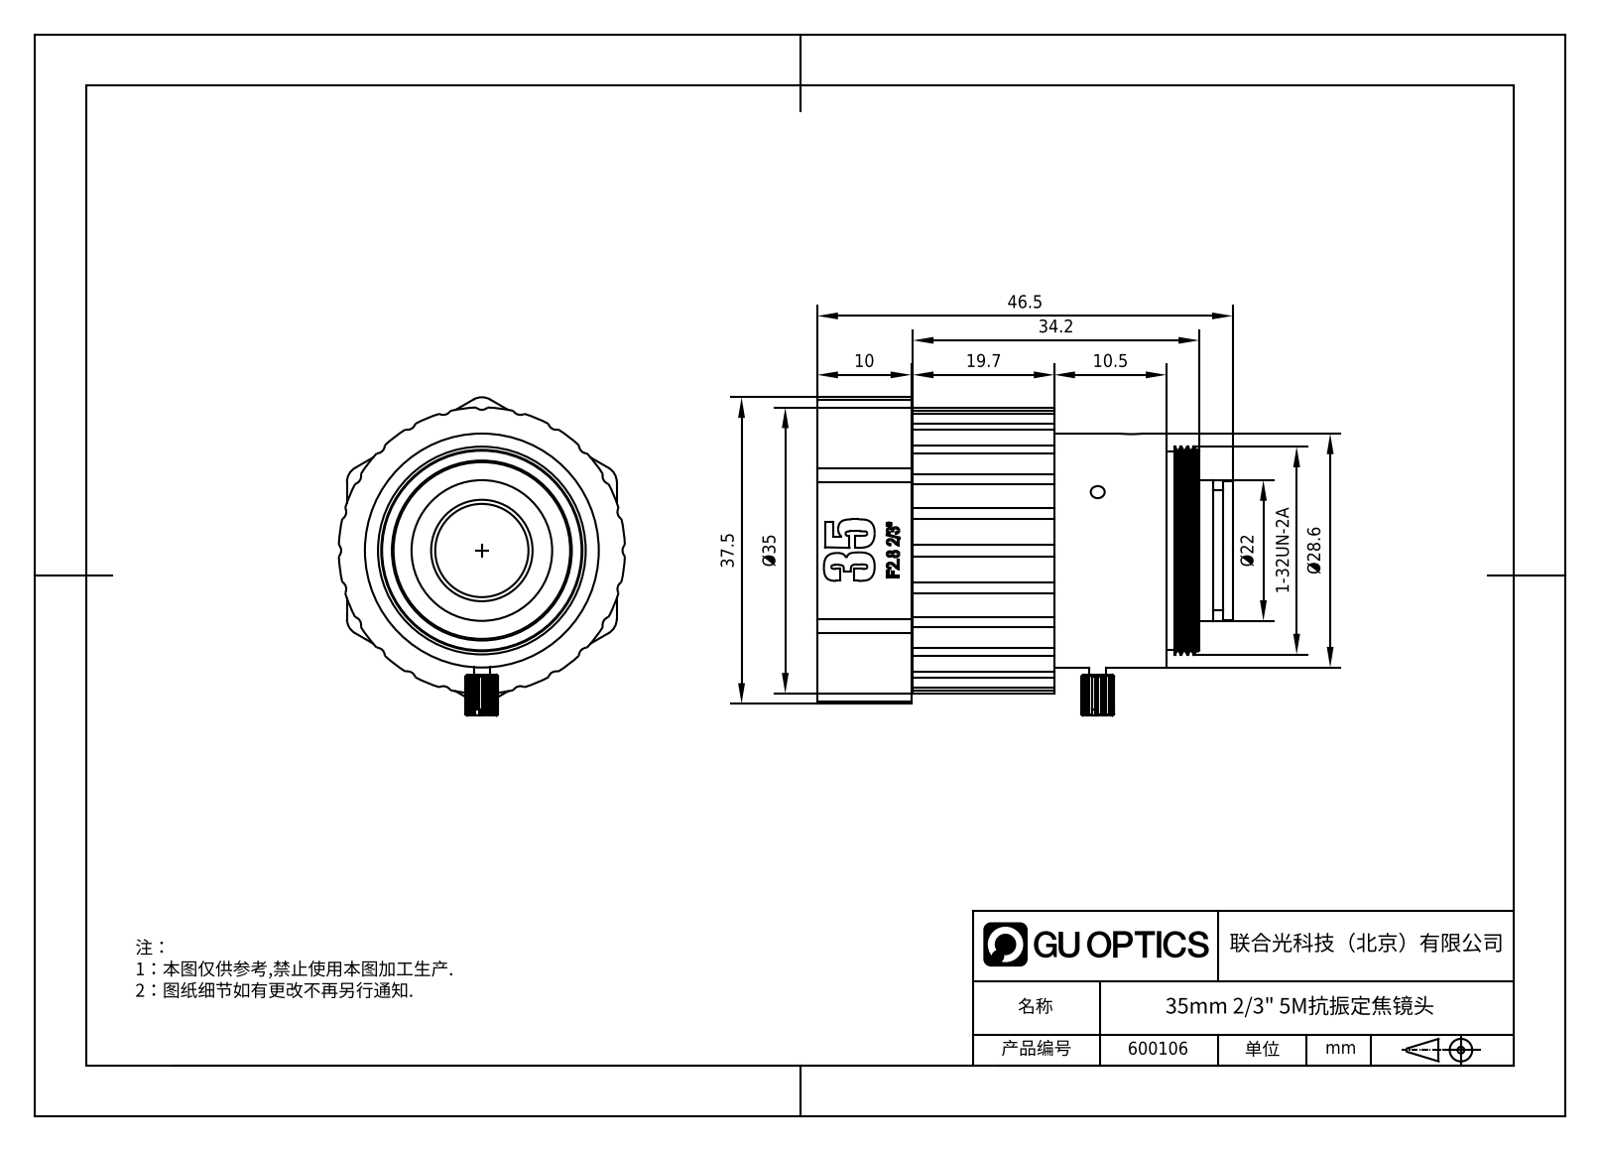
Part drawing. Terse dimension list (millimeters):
name: 600106
written by: SolidWorks 2020 (CONFIG_CONTROL_DESIGN)
unit: mm
bodies: 4 solids, 404 faces (187 planar, 114 cylindrical, 103 other)
size: 46.5 × 37.49 × 35
volume: 28 958 mm³; area: 15 713 mm²
holes: 3× ⌀2, 1× ⌀1.7, 1× ⌀2.5, 1× ⌀12, 1× ⌀13, 1× ⌀13.4, 1× ⌀16.8, 1× ⌀18.2, 1× ⌀19.5, 1× ⌀20.4, 1× ⌀25.6, 1× ⌀26.6
bosses: 1× ⌀31, 1× ⌀29.8, 1× ⌀28.6, 1× ⌀25.4, 1× ⌀24.54, 1× ⌀24.3, 1× ⌀22, 1× ⌀21.6
rounds: 24× R1, 7× R2, 1× R17.5
face distances: 10.5, 29.8, 33, 10.1, 10, 4.8, 25, 0.5, 16.7, 7.7
hole spacings: 1
